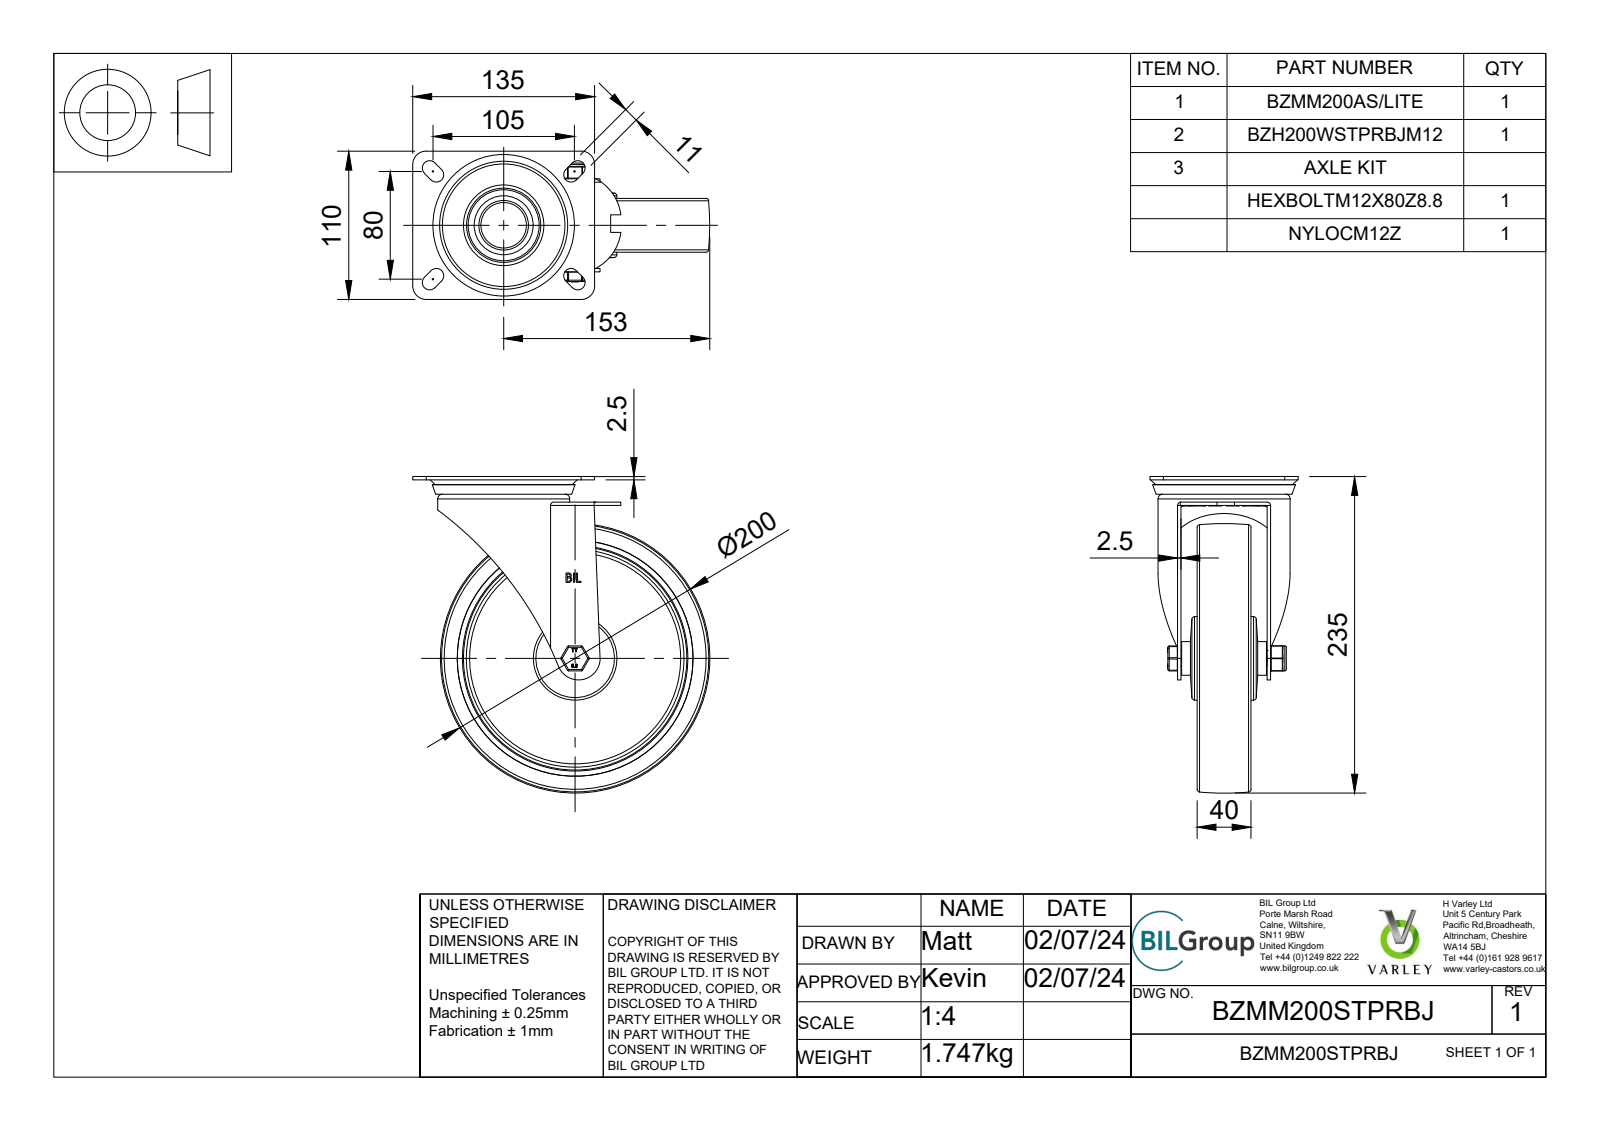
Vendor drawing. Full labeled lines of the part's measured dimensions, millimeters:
Part name (STEP PRODUCT): BZMM200STPRBJ v3; BZMM200AS/LITE - 64 v1; ZINC PLATED, PRESSED STEEL TOP PLATE (1); ZINC PLATED, PRESSED STEEL TOP PLATE Geometry (1) (+8 more)
STEP written by: Autodesk Translation Framework v13.14.0.145 (AUTOMOTIVE_DESIGN)
Units: millimetres
Bodies: 63 solids, 817 faces (316 planar, 172 cylindrical, 329 other)
Overall size (bounding box): 235 × 220.5 × 110
Volume: 777 543 mm³ · Surface area: 307 232 mm²
Round holes (diameter × count): ⌀12 ×1, ⌀12.2 ×1, ⌀12.6 ×1, ⌀14 ×1, ⌀20 ×1, ⌀28.5 ×1, ⌀30.8 ×1, ⌀33.75 ×1, ⌀40.3 ×1, ⌀40.5 ×1, ⌀42 ×1, ⌀43 ×1
Round bosses / shafts (diameter × count): ⌀98 ×1, ⌀78 ×1, ⌀62 ×1, ⌀56.5 ×1, ⌀50 ×1, ⌀48 ×1, ⌀40.8 ×1, ⌀39.75 ×1
Partial cylindrical surfaces — rounded edges, fillets, slot ends (radius × count): R0.5 ×18, R1 ×12, R5.5 ×8, R1.25 ×4, R10 ×4, R2.5 ×2, R35.15 ×2, R16 ×1
Main face-to-face distances: 6.5, 16.75, 2.5, 23.25, 12, 14.5, 37.75, 28.75, 35.25, 52
